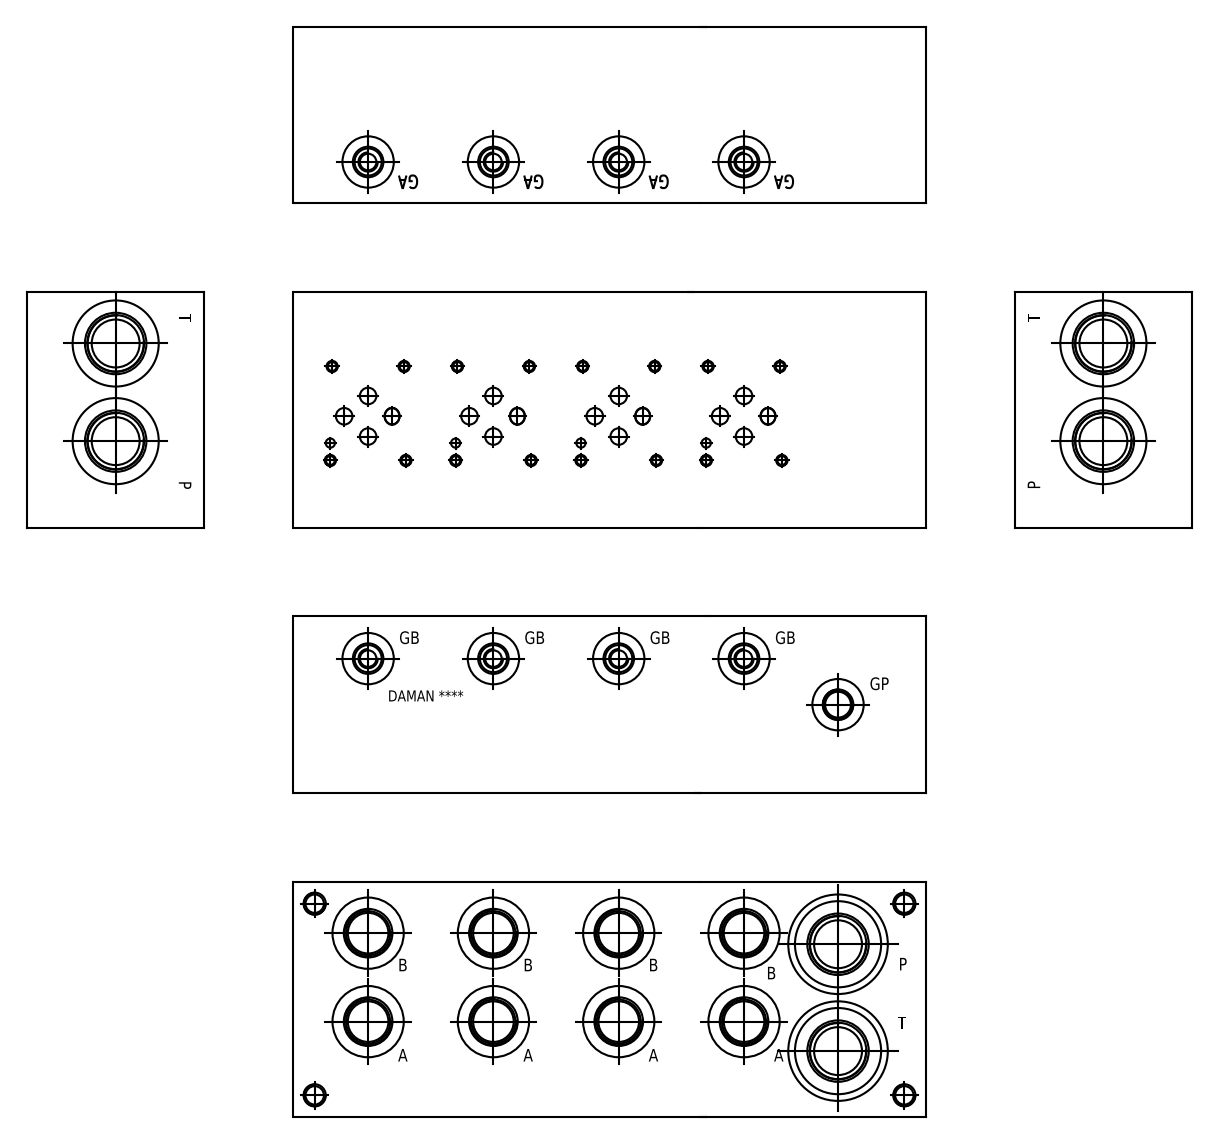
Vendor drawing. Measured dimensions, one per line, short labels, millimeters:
name: Part_AD03PB042B_3D
written by: Autodesk Inventor 2020 (AUTOMOTIVE_DESIGN)
unit: mm
bodies: 1 solid, 1271 faces (655 planar, 154 cylindrical, 462 other)
size: 273.05 × 101.6 × 76.2
volume: 1 899 000 mm³; area: 156 008 mm²
holes: 20× ⌀7.14, 16× ⌀4.22, 16× ⌀5, 9× ⌀11.68, 9× ⌀13.26, 9× ⌀22.12, 8× ⌀17.48, 8× ⌀18.92, 8× ⌀21.06, 8× ⌀30.68, 4× ⌀3.96, 4× ⌀6.35
face distances: 101.6, 76.2, 0.79, 273.05, 75.41, 100.81, 272.26, 271.47, 5.56, 4.77
hole spacings: 53.97, 107.95, 53.98, 161.92, 40.5, 51.45, 49.71, 0.4
